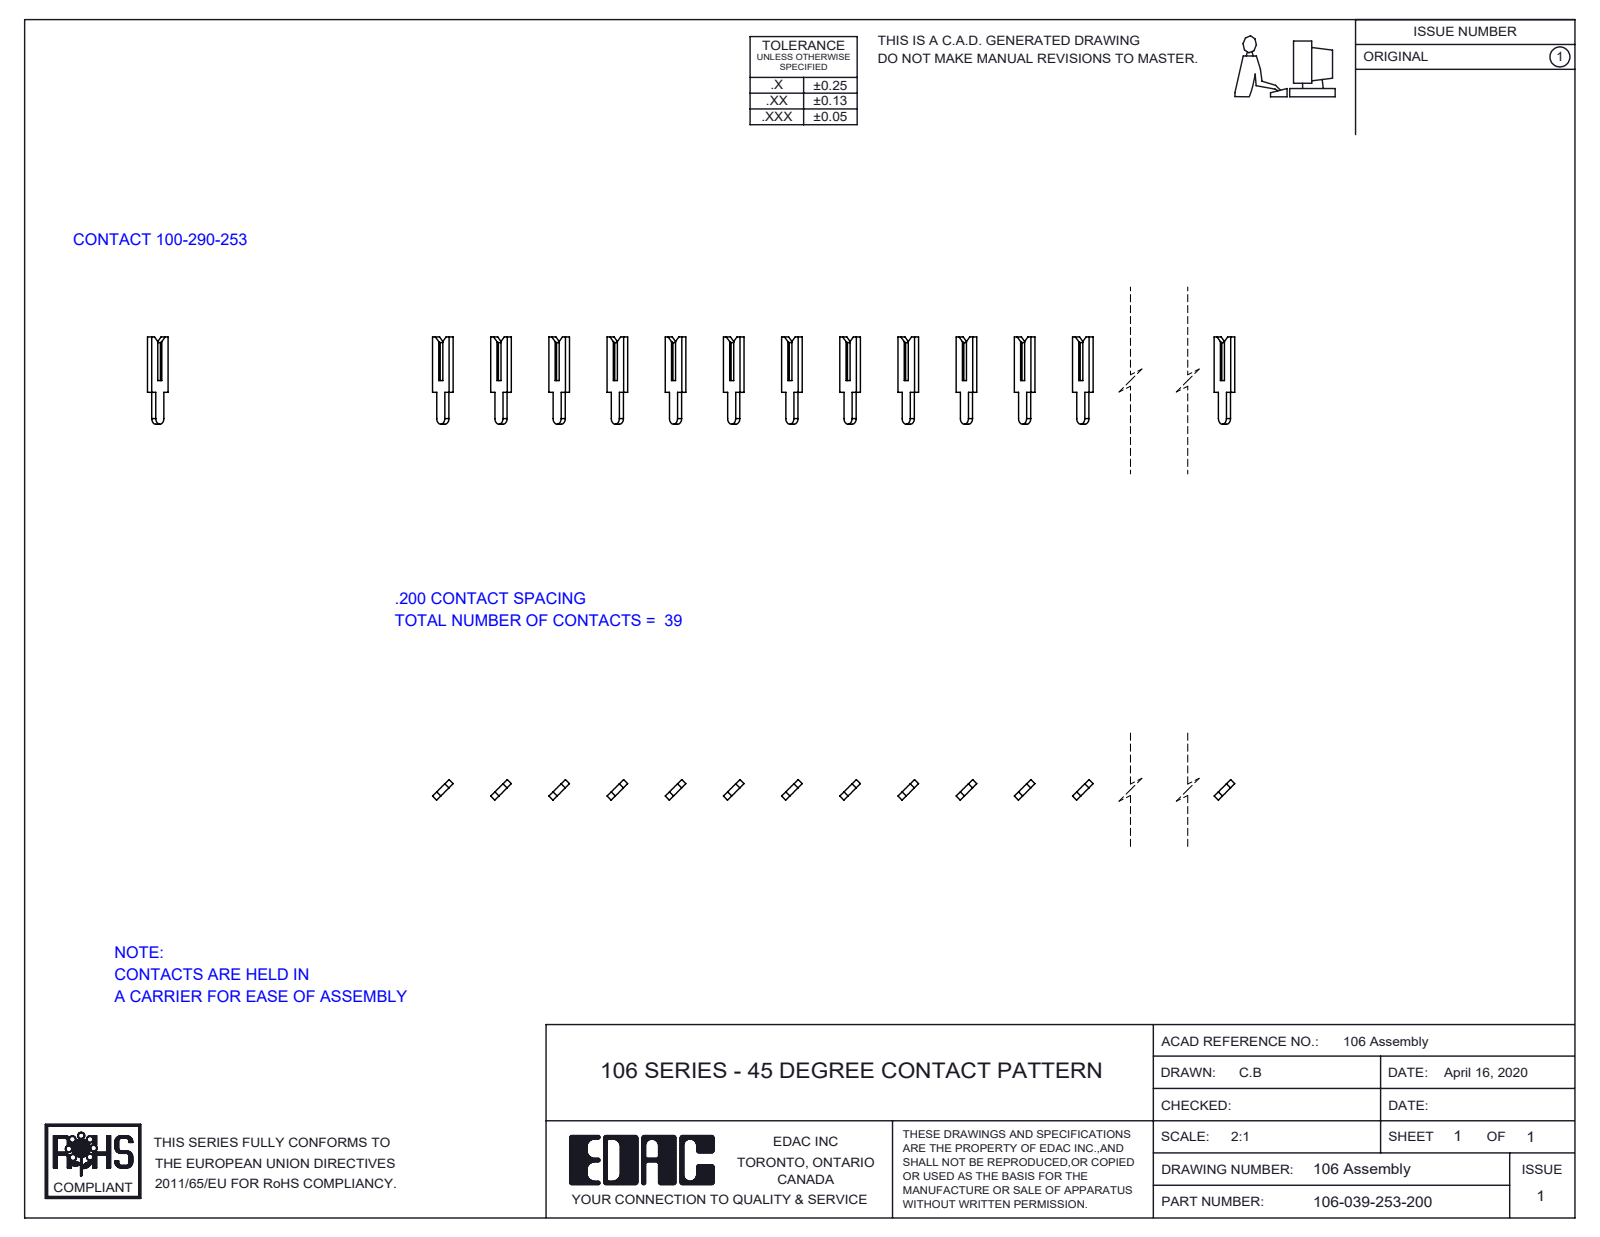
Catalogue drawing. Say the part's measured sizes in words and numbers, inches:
The part is named "106-039-253-200; 100-290-001_100-290-253". Its 3-D file was written by "SolidWorks 2016 (CONFIG_CONTROL_DESIGN)". It is 39 solids with 780 faces: 741 planar, 39 cylindrical and 0 other. Overall it measures 7.671 by 0.3 by 0.071 inches. Its volume is 0.013 cubic inches and its surface area 2.08 square inches. Partial cylindrical surfaces (rounded edges, fillets, slot ends): 39 of radius 0.019. The main face-to-face distances are 0.141, 0.848, 0.283, 0.99, 0.707, 0.566, 0.424, 1.131, 0.424, 1.838.
